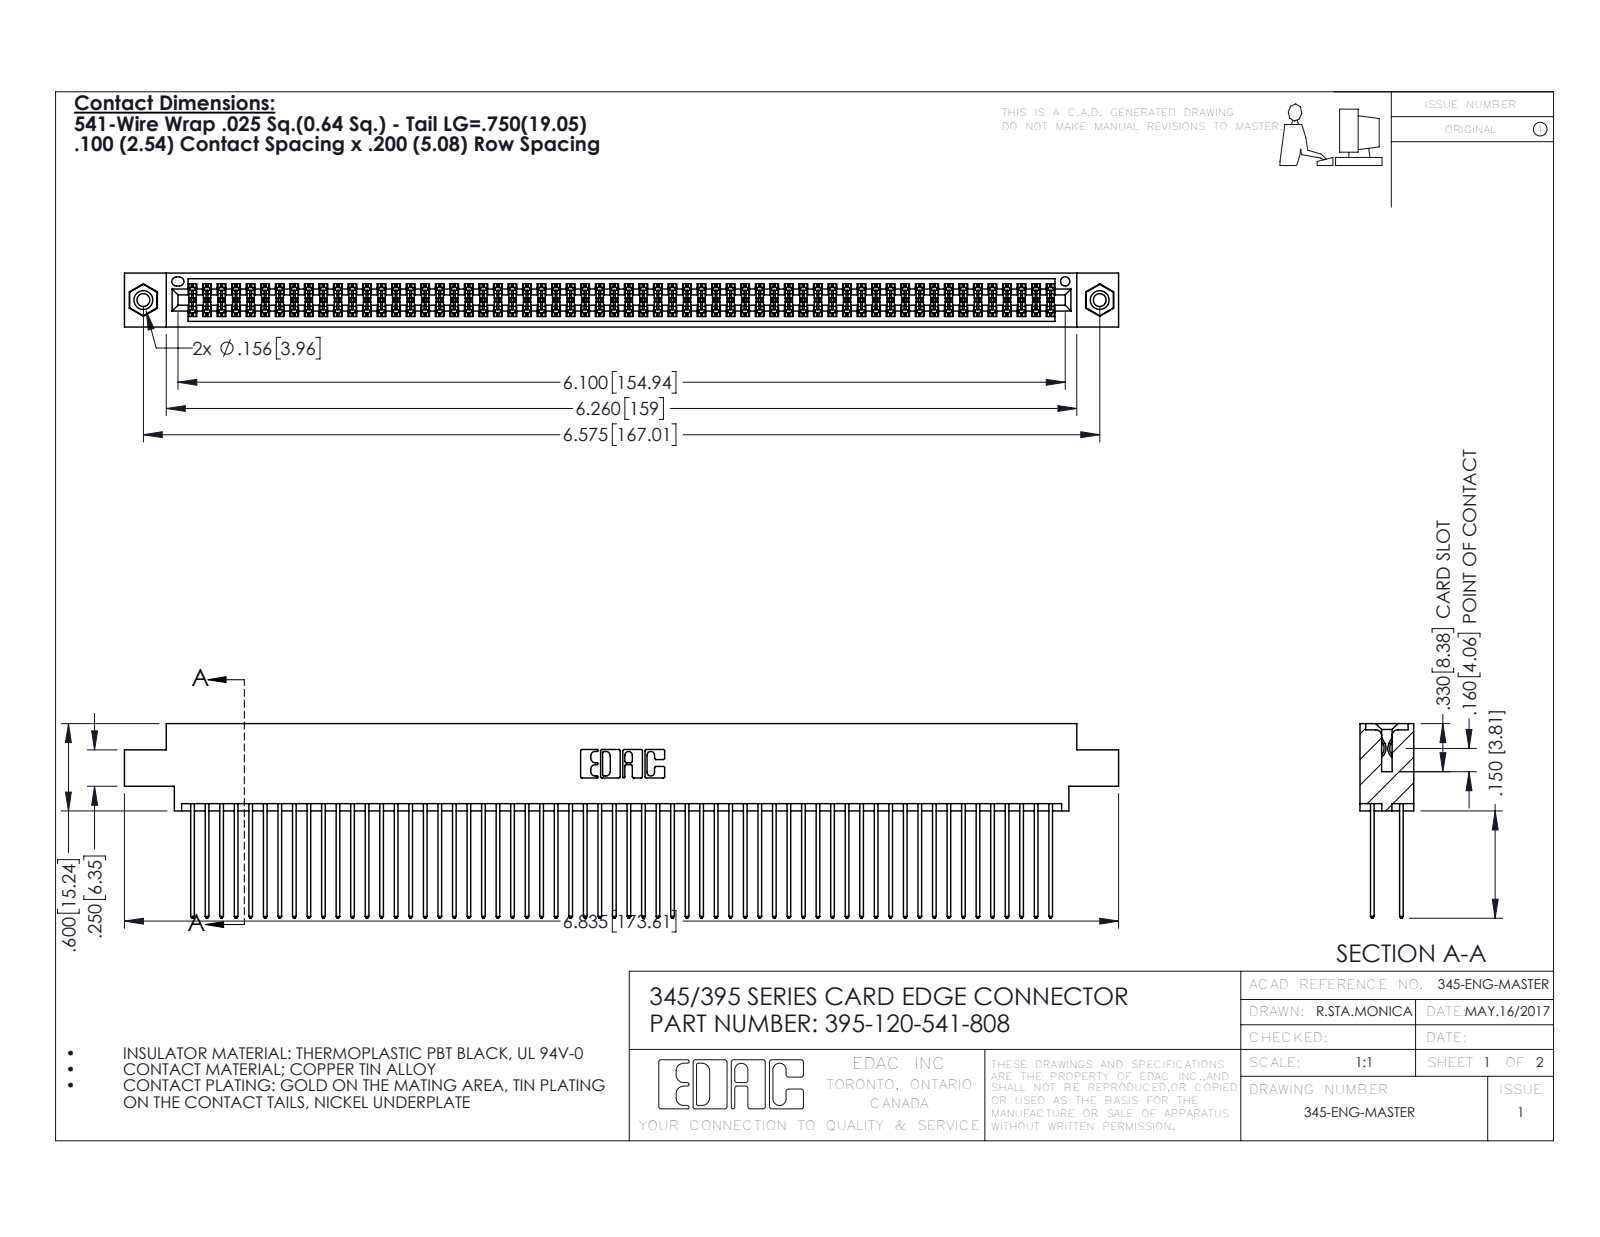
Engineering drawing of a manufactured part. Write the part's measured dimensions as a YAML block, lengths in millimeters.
part_name: "345-250-001_345-250-003-102; 395-120-541-808; 345-292-001_345-293-141; 345 Part_0.170 Offset - 0.156 Dia-TI"
step_written_by: "SolidWorks 2016 (CONFIG_CONTROL_DESIGN)"
units: millimeters
bodies: {solids: 123, faces: 6190, planar: 4076, cylindrical: 2098, other: 16}
overall_size: [173.6, 34, 9.4]
volume: 17600
surface_area: 29750
round_holes:
  - {diameter: 2.3, count: 2}
  - {diameter: 3.2, count: 2}
  - {diameter: 4, count: 2}
  - {diameter: 1.6, count: 1}
round_bosses_or_shafts:
  - {diameter: 3.9, count: 2}
partial_cylinders:
  - {radius: 0.2, count: 180}
  - {radius: 0.3, count: 120}
  - {radius: 0.3, count: 22}
  - {radius: 0.2, count: 6}
  - {radius: 0.8, count: 6}
  - {radius: 0.7, count: 3}
  - {radius: 0.4, count: 2}
  - {radius: 0.5, count: 2}
face_to_face_distances: [1.8, 7.6, 5.1, 2.5, 6.9, 0.6, 5.7, 9.4, 4.4, 3.8]
hole_center_spacings: [6.9, 161, 167]
